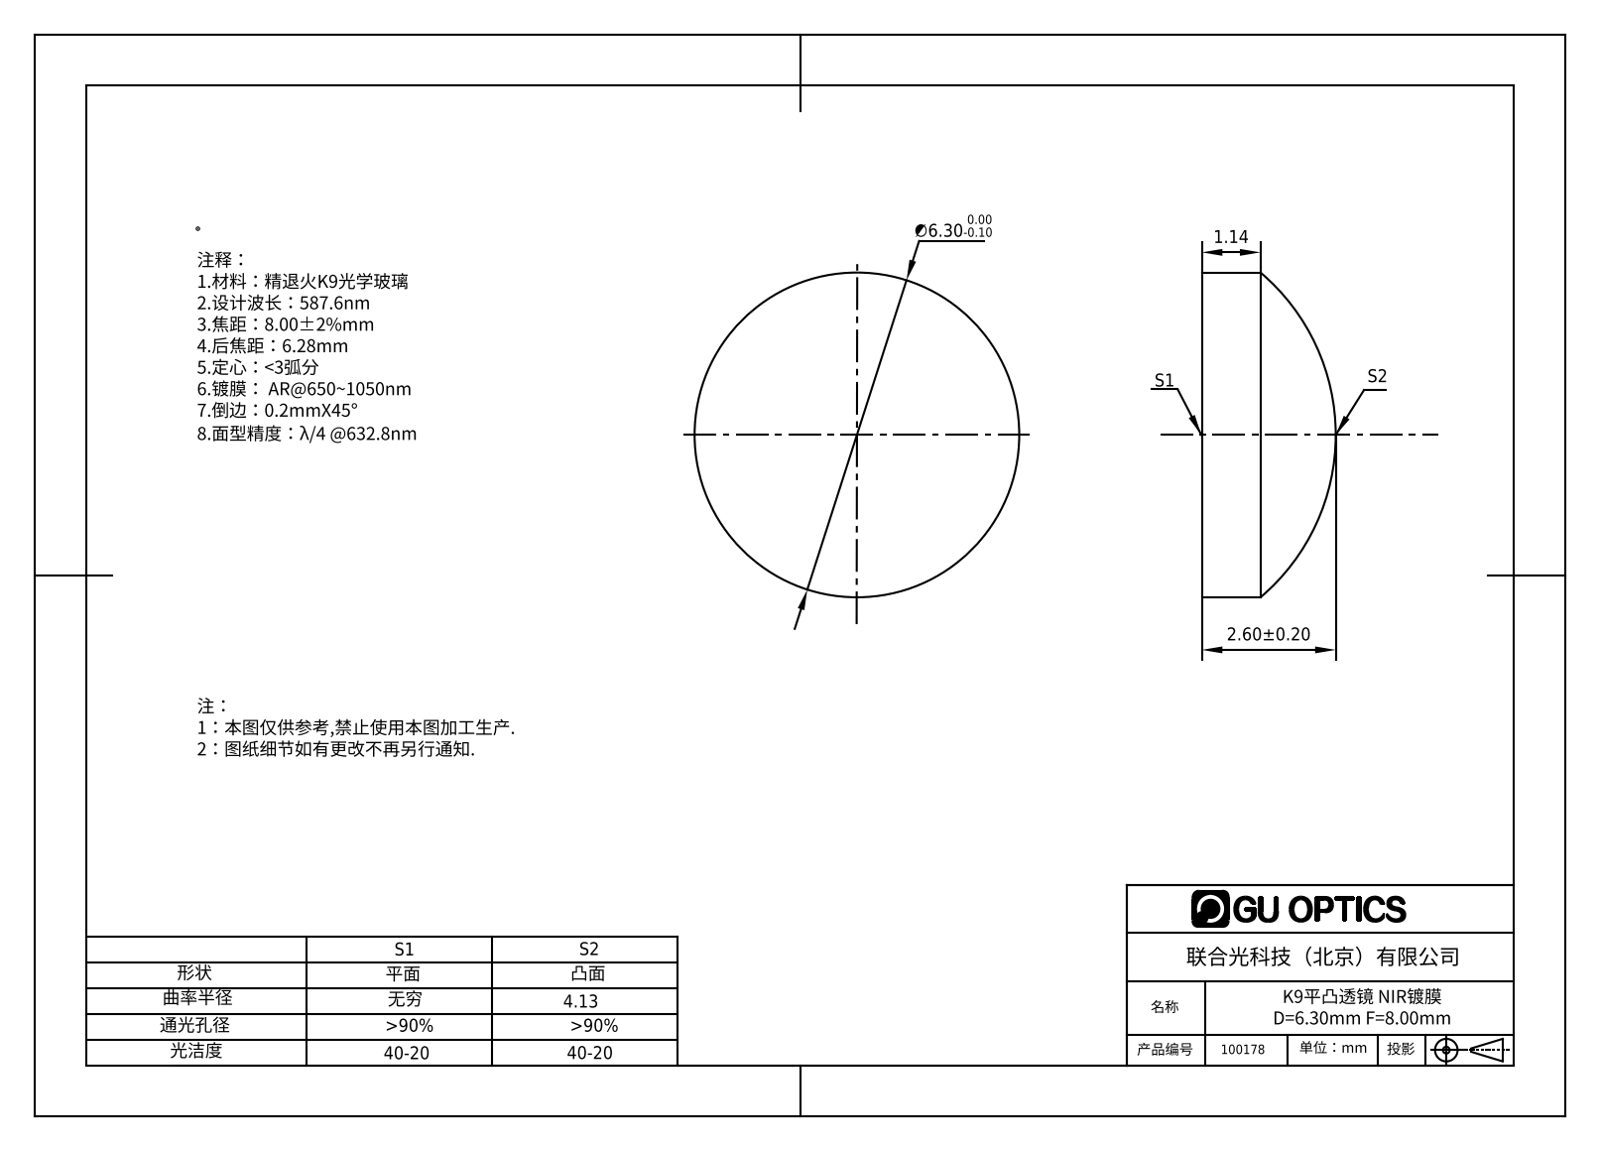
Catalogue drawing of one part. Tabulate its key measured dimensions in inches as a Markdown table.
| quantity | value |
| --- | --- |
| part name | 100178 |
| STEP written by | SolidWorks 2016 (AUTOMOTIVE_DESIGN) |
| units | inches |
| bodies | 1 solid, 5 faces (1 planar, 2 cylindrical, 2 other) |
| overall size | 0.248 × 0.248 × 0.102 |
| volume | 0.004 in³ |
| surface area | 0.14 in² |
| round bosses / shafts (diameter × count) | 0.248 × 1 |
